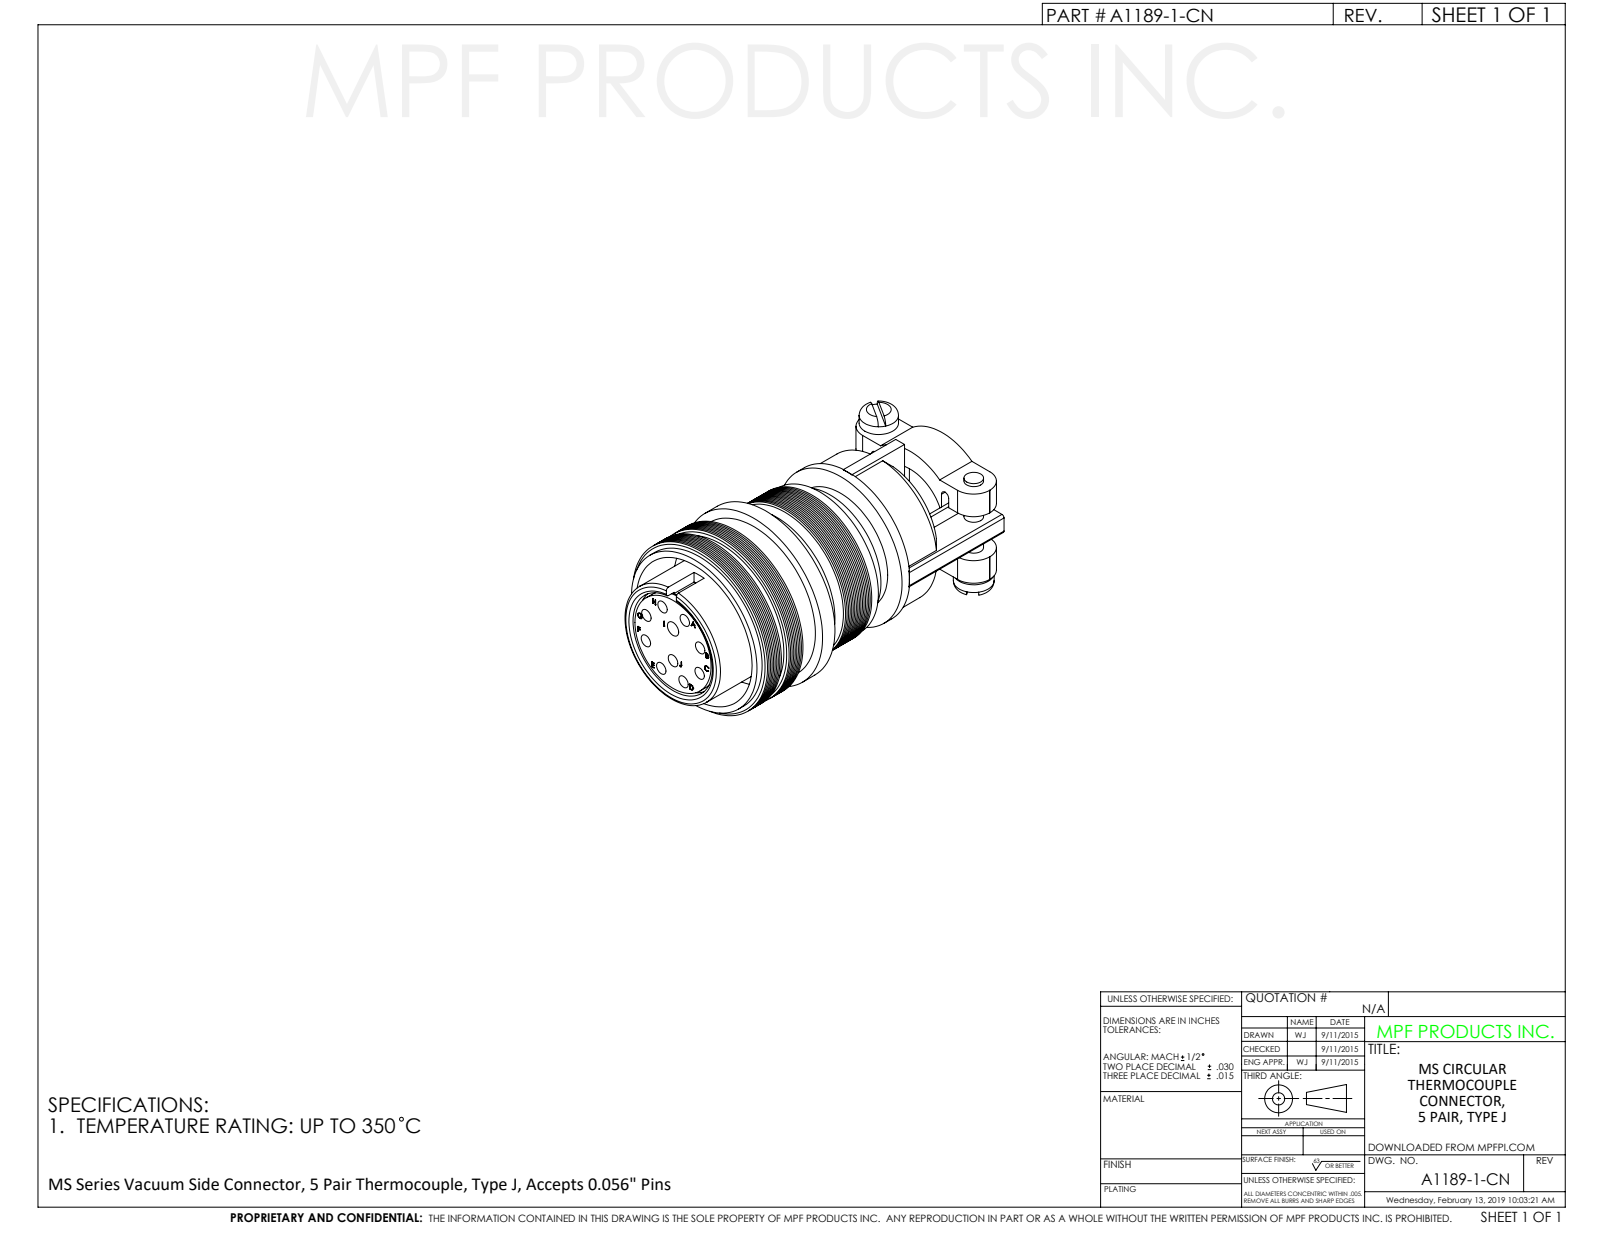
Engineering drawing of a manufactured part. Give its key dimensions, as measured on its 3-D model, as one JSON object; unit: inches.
{"part_name": "A1189-1", "step_written_by": "SolidWorks 2019 (CONFIG_CONTROL_DESIGN)", "units": "inches", "bodies": {"solids": 1, "faces": 658, "planar": 292, "cylindrical": 118, "other": 248}, "overall_size": [2.637, 1.34, 1.34], "volume_in3": 2.225, "surface_area_in2": 23.28, "round_holes": [[0.076, 10], [0.021, 1], [0.026, 1], [0.029, 1], [0.031, 1], [0.78, 1], [1.125, 1]], "round_bosses_or_shafts": [[0.135, 2], [1.34, 1], [1.223, 1], [1.22, 1], [1.2, 1], [1.14, 1], [0.99, 1], [0.92, 1]], "partial_cylinders_radius": [[0.034, 8], [0.02, 4], [0.156, 4], [0.313, 1], [0.323, 1], [0.472, 1], [0.473, 1]], "face_to_face_distances": [1.193, 0.643, 0.47, 0.722, 0.1, 0.2, 0.522, 0.992, 1.714, 2.618], "hole_center_spacings": [0.056, 0.062, 0.07, 0.074, 0.113, 0.125, 0.127, 0.177]}
